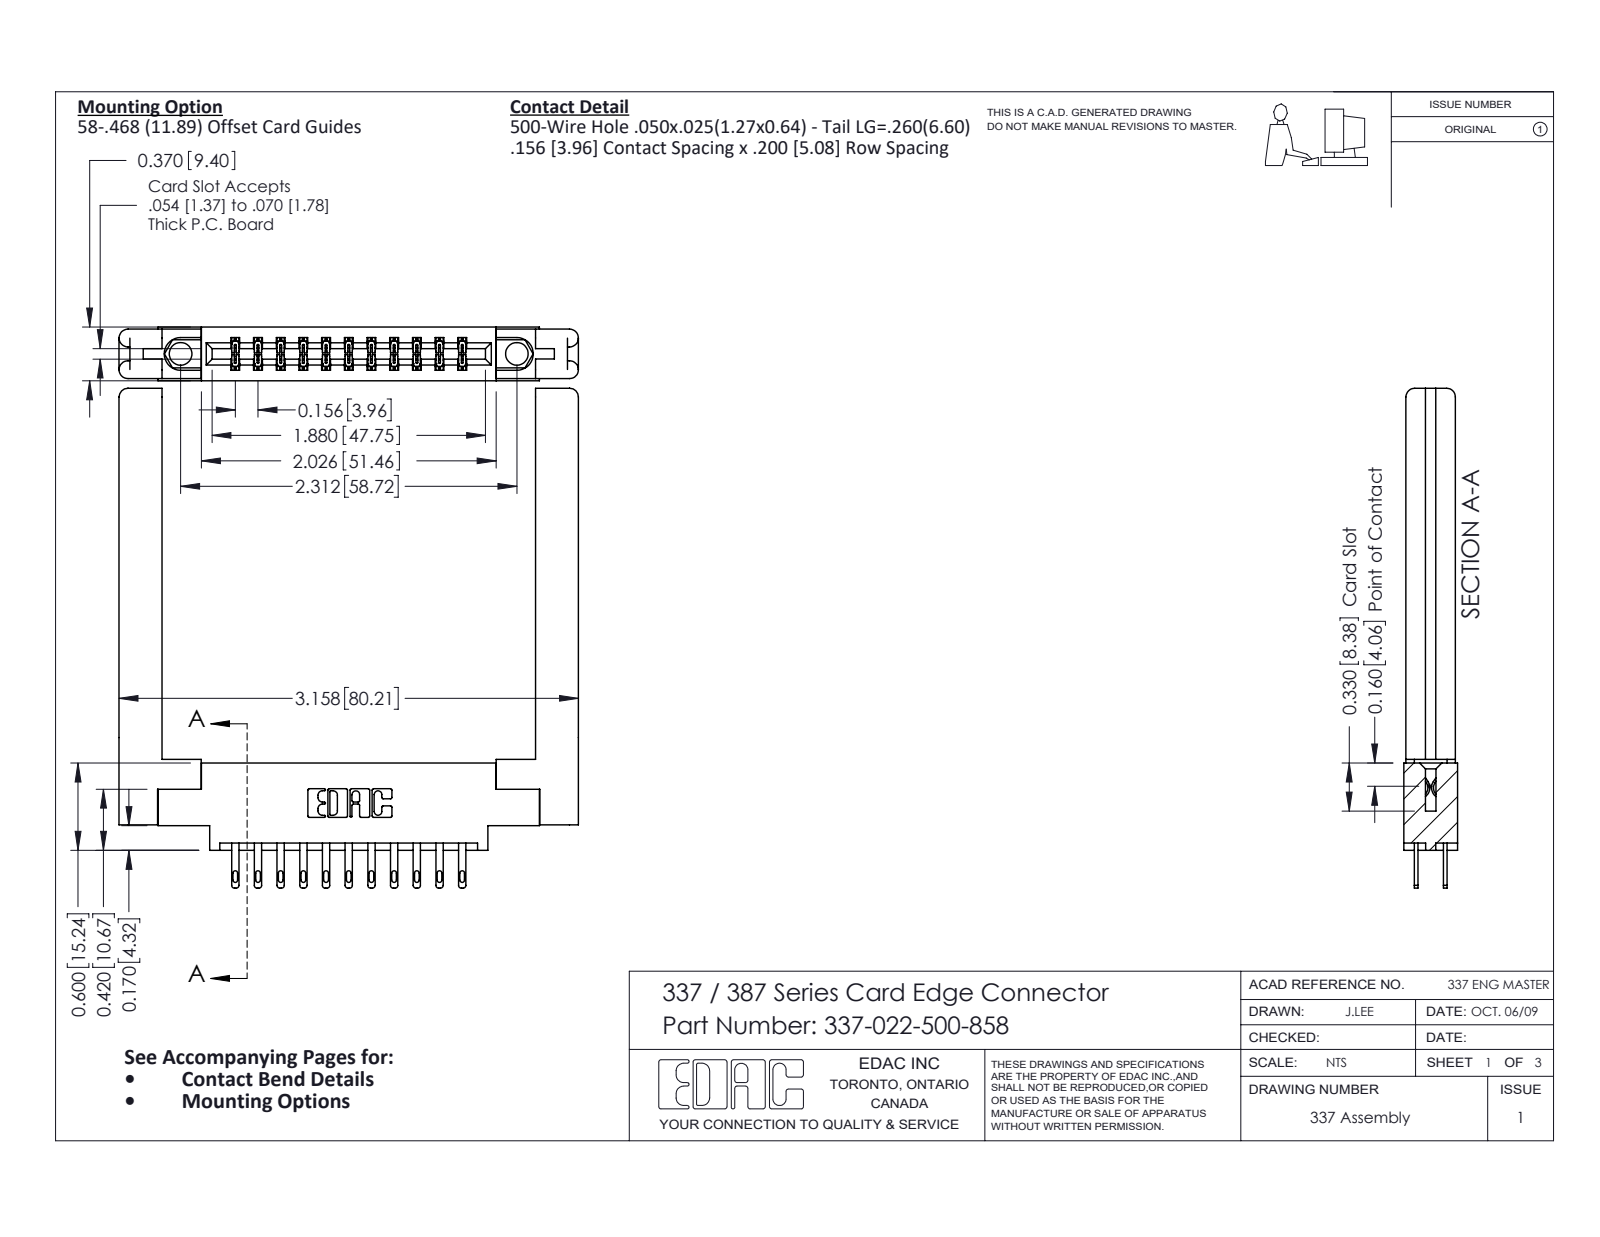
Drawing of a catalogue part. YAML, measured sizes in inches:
part_name: "337-022-500-858; 345-250-001_345-250-001-102; 345-292-001_345-293-100; 337 Part_0.170 Offset - 0.156 Dia-TI (+1 more)"
step_written_by: "SolidWorks 2016 (CONFIG_CONTROL_DESIGN)"
units: inches
bodies: {solids: 27, faces: 1360, planar: 862, cylindrical: 474, other: 24}
overall_size: [3.435, 3.158, 0.37]
volume: 0.923
surface_area: 21.9
round_holes:
  - {diameter: 0.089, count: 2}
  - {diameter: 0.125, count: 2}
  - {diameter: 0.156, count: 2}
round_bosses_or_shafts:
  - {diameter: 0.155, count: 2}
partial_cylinders:
  - {radius: 0.006, count: 33}
  - {radius: 0.01, count: 22}
  - {radius: 0.016, count: 22}
  - {radius: 0.02, count: 22}
  - {radius: 0.061, count: 8}
  - {radius: 0.007, count: 6}
  - {radius: 0.031, count: 6}
  - {radius: 0.06, count: 5}
face_to_face_distances: [0.355, 0.015, 0.37, 0.34, 0.135, 0.072, 0.148, 0.15, 0.298, 0.057]
hole_center_spacings: [2.312]
